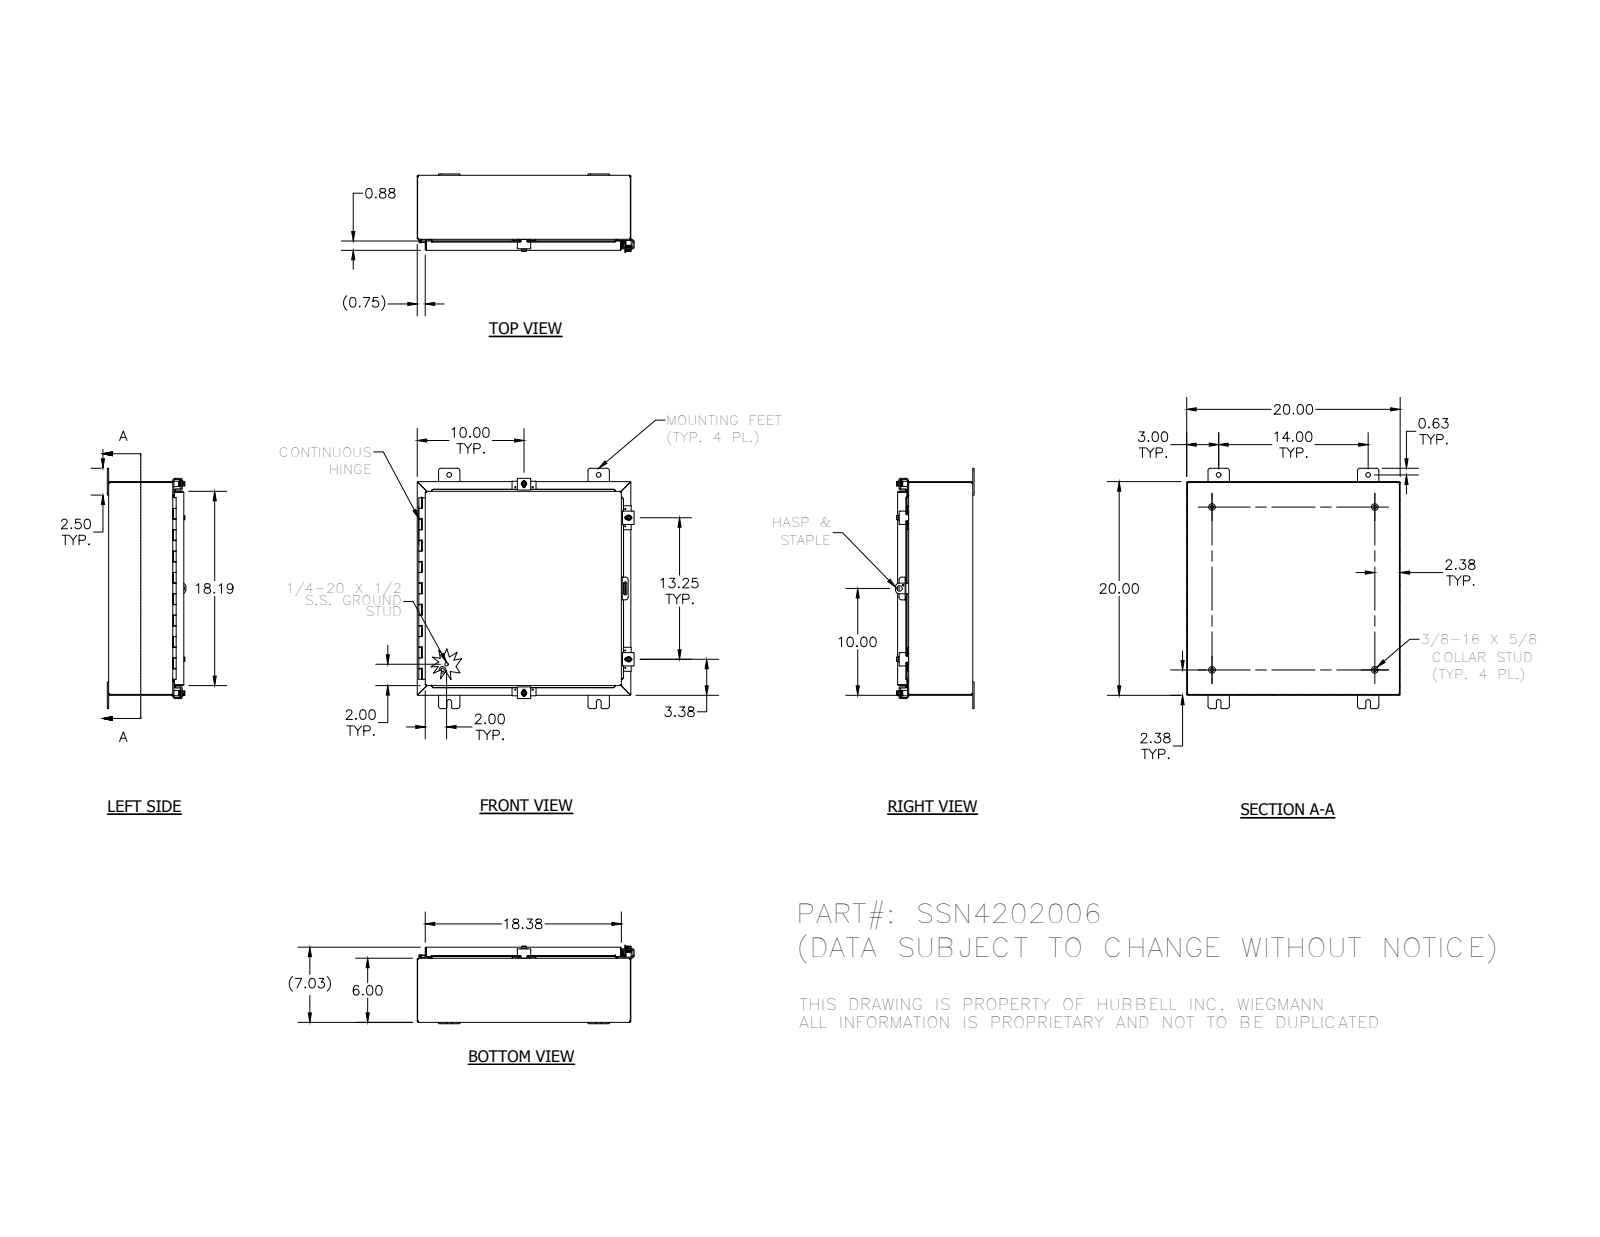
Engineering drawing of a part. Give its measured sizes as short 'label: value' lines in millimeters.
name: SSN4202006; 30818_1; 328137T_1; SSN4202006BKP_1 (+8 more)
written by: SolidWorks 2014 (AUTOMOTIVE_DESIGN)
unit: mm
bodies: 37 solids, 1444 faces (567 planar, 632 cylindrical, 245 other)
size: 571.5 × 515.9 × 186.8
volume: 1 991 000 mm³; area: 2 043 000 mm²
holes: 8× ⌀2.8, 4× ⌀5.4, 4× ⌀7.1, 4× ⌀7.6, 4× ⌀11.1, 1× ⌀3.2, 1× ⌀4, 1× ⌀12.7
bosses: 6× ⌀6.4, 4× ⌀15.9, 4× ⌀13.2, 4× ⌀12.7, 4× ⌀8.9, 4× ⌀8.4, 2× ⌀2.9, 1× ⌀8.6
rounds: 49× R0.8, 33× R3.2, 29× R6.4, 23× R0.8, 23× R2.7, 11× R1.6, 8× R1.8, 8× R3.6
face distances: 1.9, 176.8, 506.1, 174.9, 178.6, 504.2, 508, 150.5, 26.2, 152.4
hole spacings: 22.3, 490.4, 336.6, 22.3, 41.3, 41.3, 157.2, 159.8
